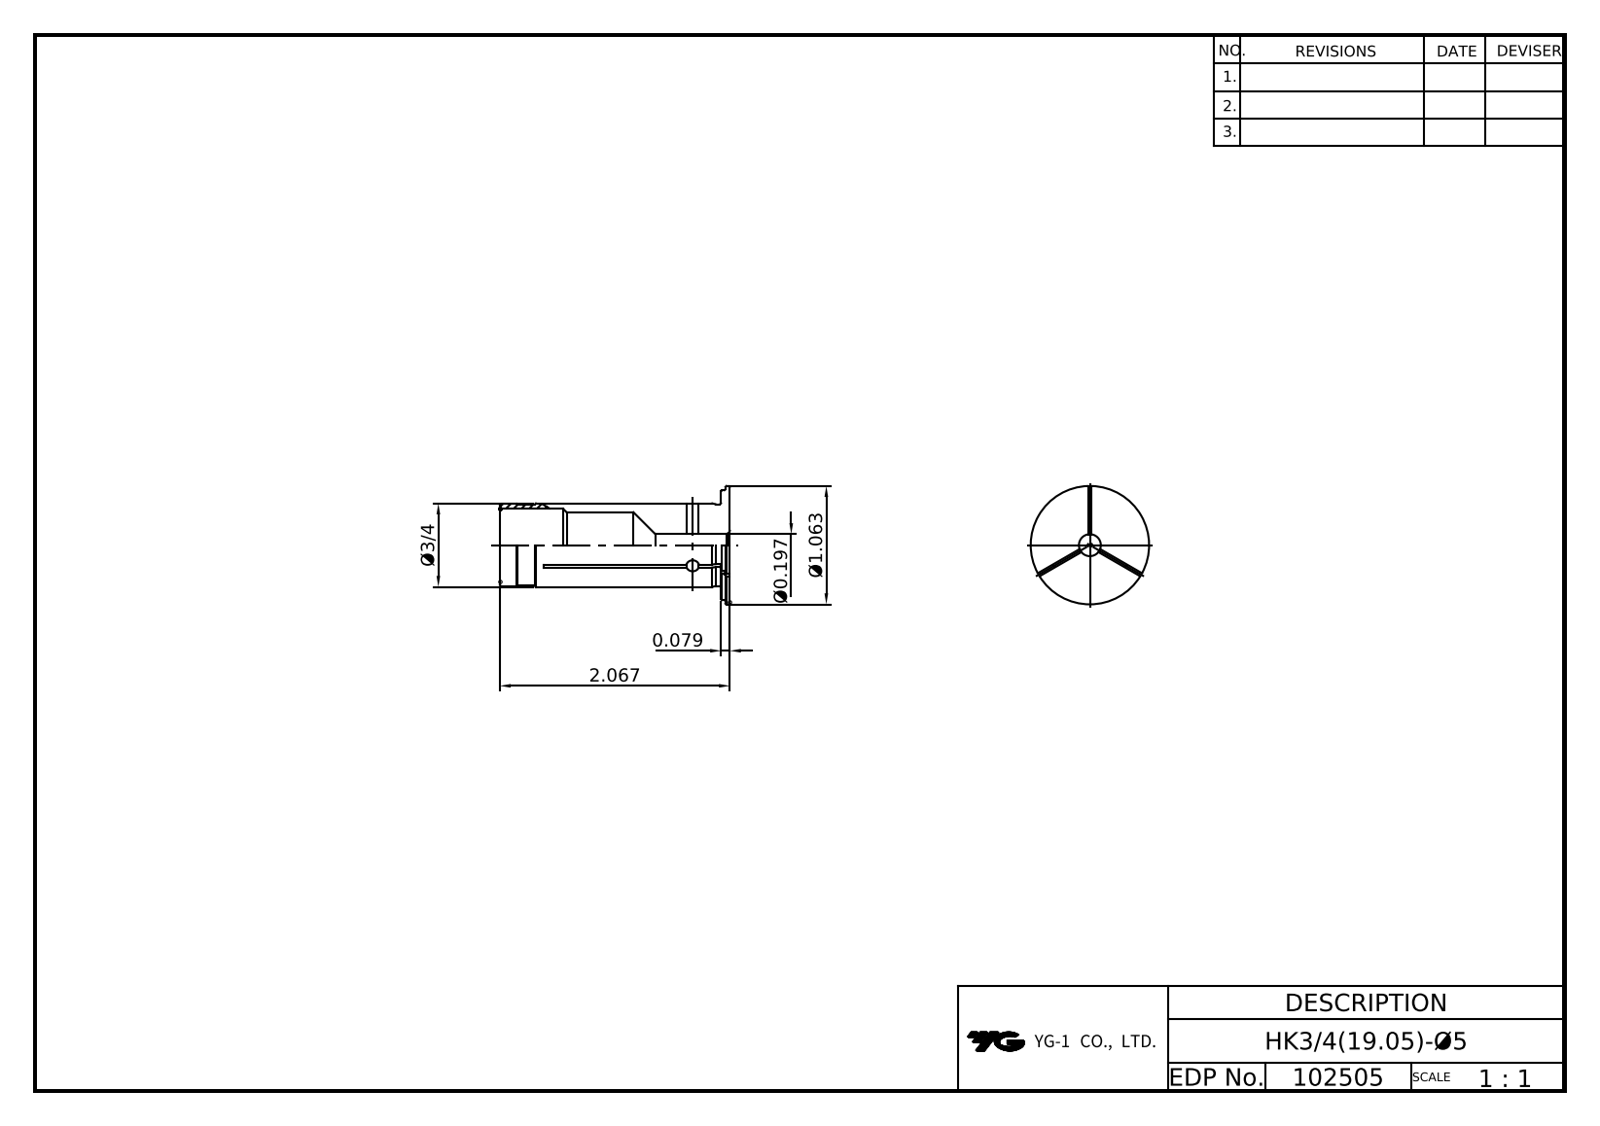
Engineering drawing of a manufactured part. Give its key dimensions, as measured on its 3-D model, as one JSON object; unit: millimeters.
{"part_name": "LO-HK19.05-5", "step_written_by": "Autodesk Inventor 2025 (AP242_MANAGED_MODEL_BASED_3D_ENGINEERING_MIM_LF)", "units": "millimeters", "bodies": {"solids": 1, "faces": 12, "planar": 4, "cylindrical": 6, "other": 2}, "overall_size": [52.5, 27, 27], "volume_mm3": 8756, "surface_area_mm2": 6109, "round_holes": [[5, 1], [15, 1], [16.5, 1]], "round_bosses_or_shafts": [[27, 1], [25, 1], [19.05, 1]], "face_to_face_distances": [2, 1, 50.5, 51.5, 52.5]}
